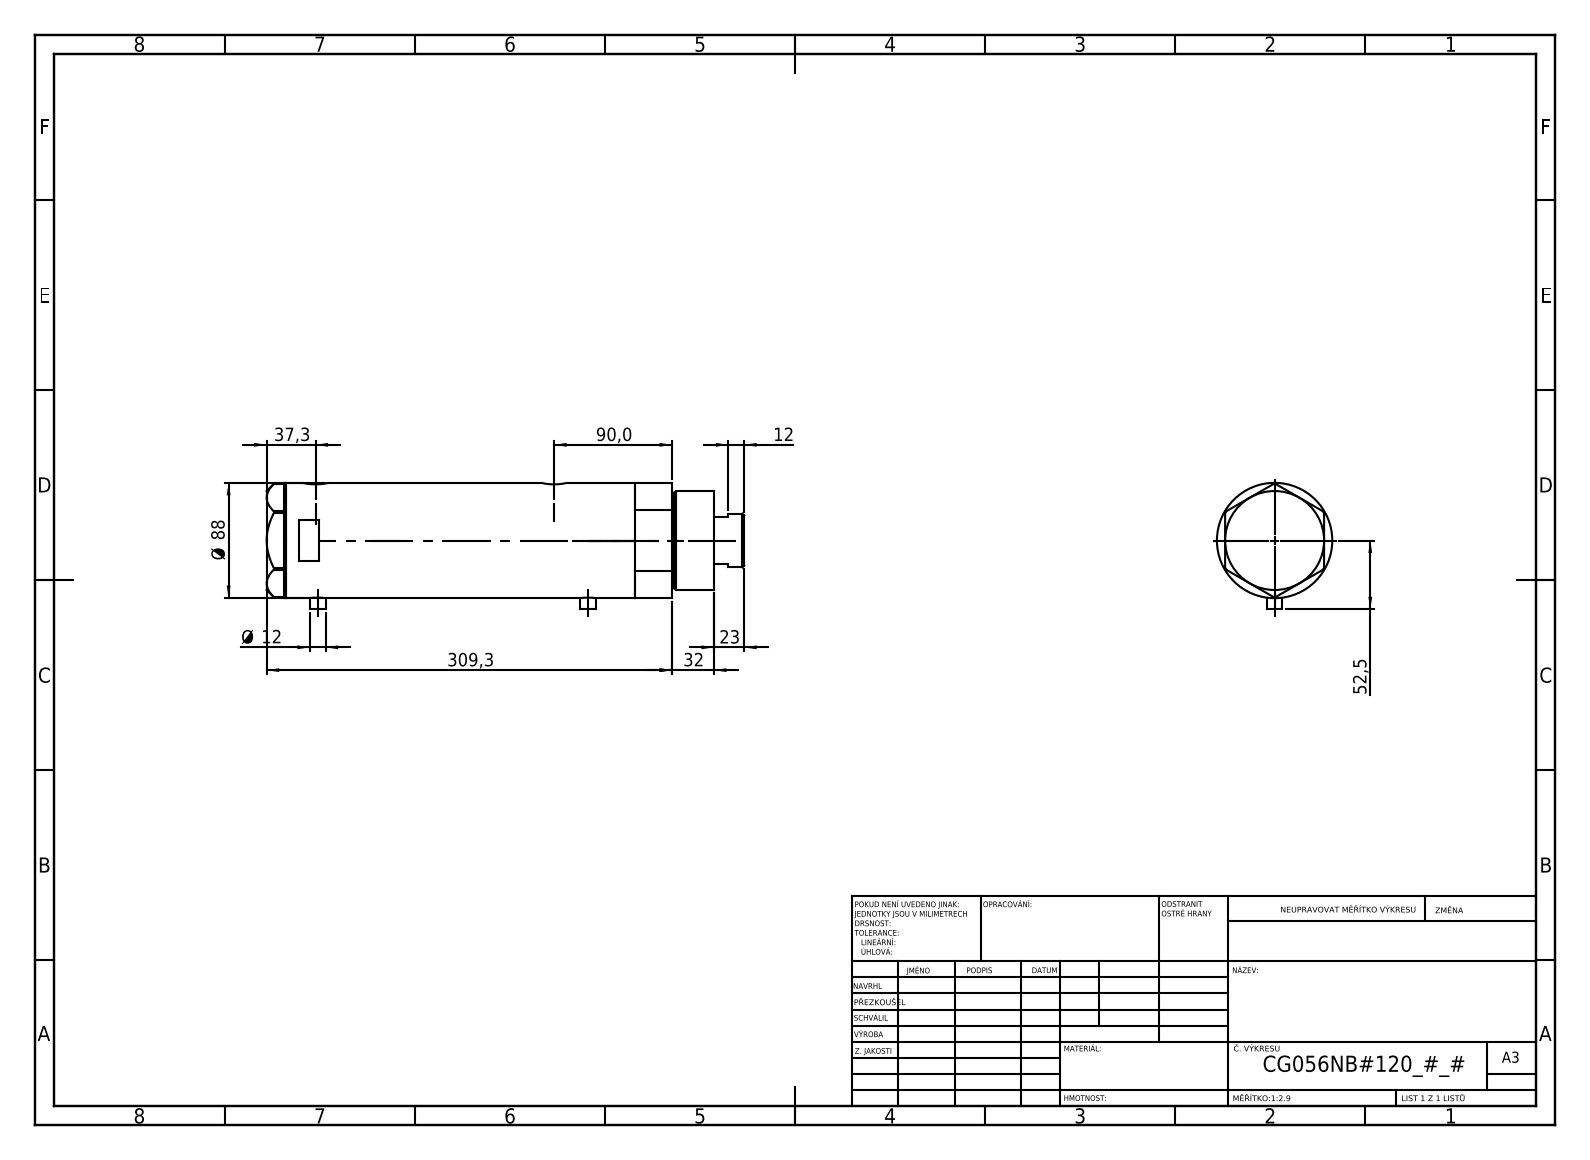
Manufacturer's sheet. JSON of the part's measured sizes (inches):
{"part_name": "V270CG_FRONT; V270CG_BACK; V270CG_VC; V270CG_MIDDLE", "step_written_by": "SolidWorks 2019 (CONFIG_CONTROL_DESIGN)", "units": "inches", "bodies": {"solids": 4, "faces": 121, "planar": 52, "cylindrical": 49, "other": 20}, "overall_size": [14.343, 3.799, 3.465], "volume_in3": 115, "surface_area_in2": 406.6, "round_holes": [[0.492, 2], [0.518, 2], [0.787, 2], [0.571, 1], [1.654, 1], [1.713, 1], [2.205, 1], [2.362, 1], [3.15, 1]], "round_bosses_or_shafts": [[0.472, 2], [3.465, 1], [2.953, 1], [2.874, 1], [1.614, 1]], "face_to_face_distances": [8.047, 1.024, 7.024, 0.591, 1.614, 8.638, 12.846, 13.437, 11.823, 4.799], "hole_center_spacings": [0.067, 1.016, 7.098, 7.165, 8.114, 8.181]}
